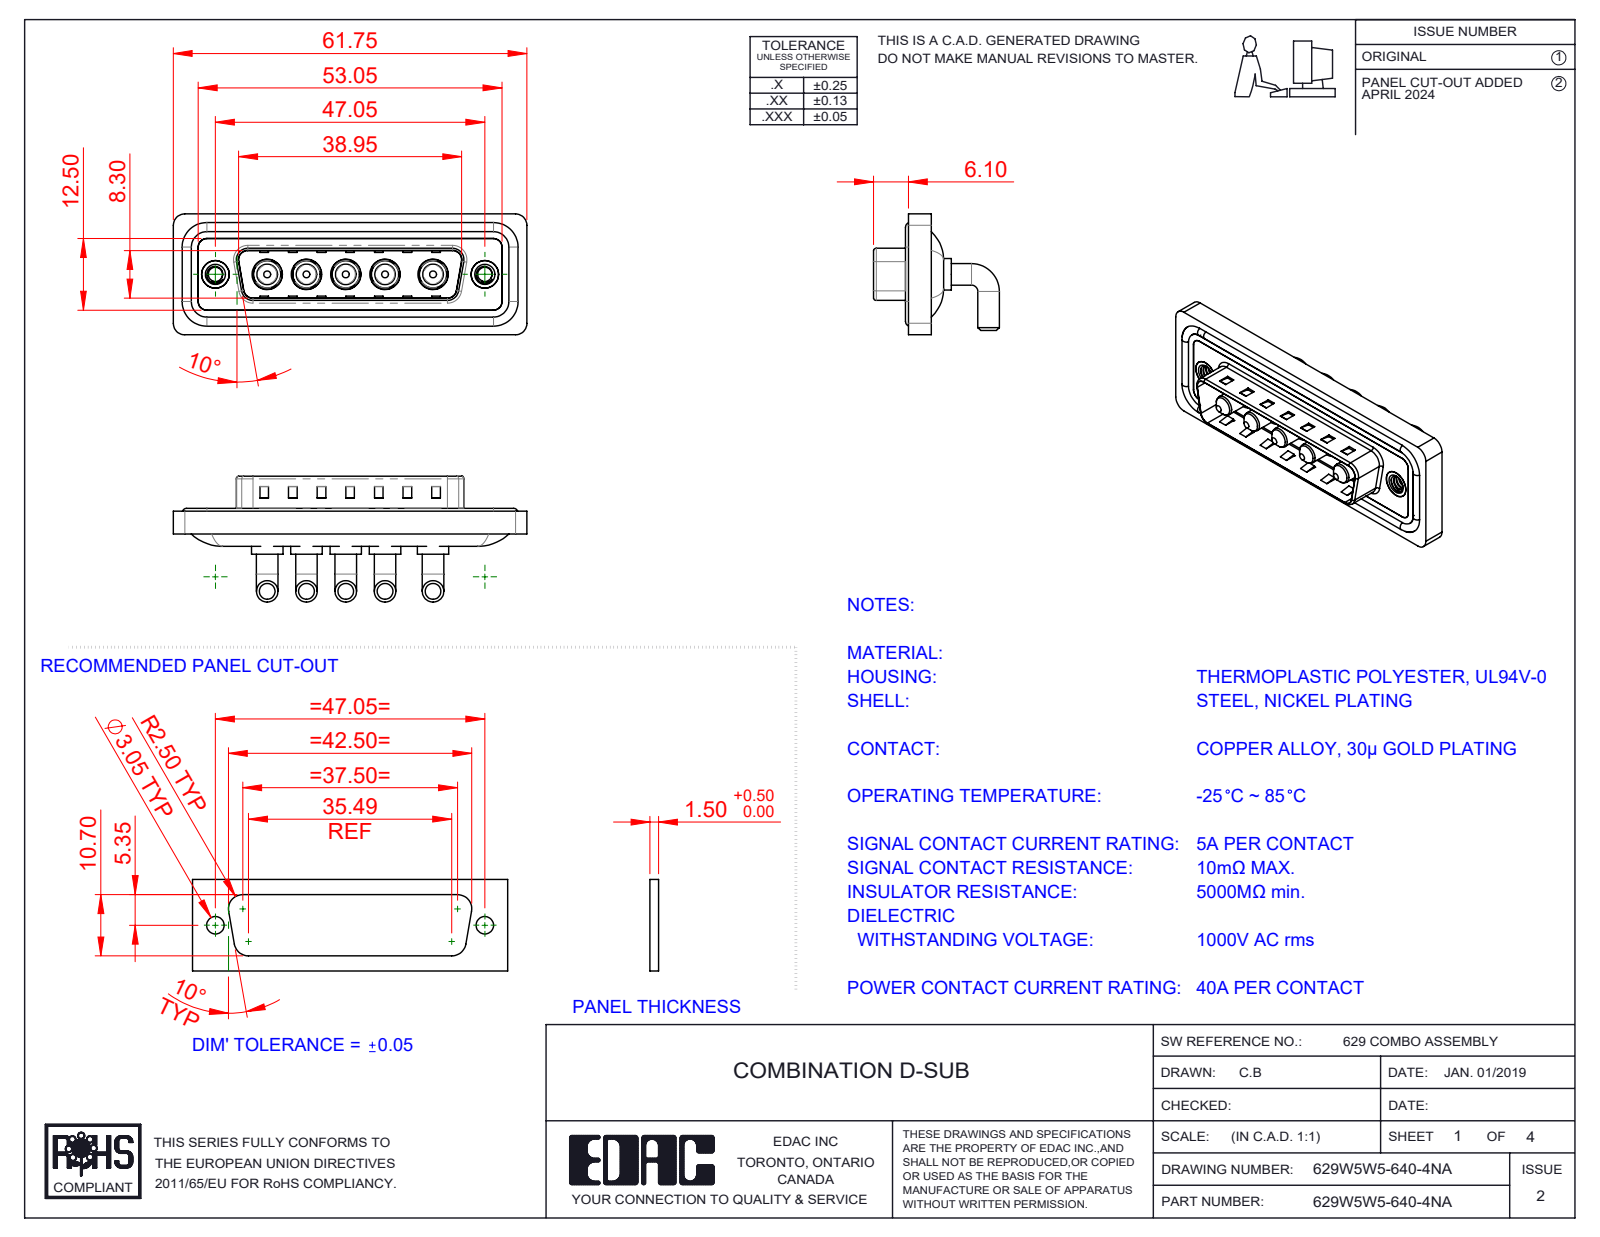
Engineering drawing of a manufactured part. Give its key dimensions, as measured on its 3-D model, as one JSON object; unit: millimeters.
{"part_name": "629Combo Shell Rear_25 Contacts; 629Combo Threaded Rivet_A; 629Combo Waterproof Housing_25 Contacts; 629Combo Shell Front_25 Contacts (+3 more)", "step_written_by": "SolidWorks 2023 (CONFIG_CONTROL_DESIGN)", "units": "millimeters", "bodies": {"solids": 17, "faces": 692, "planar": 259, "cylindrical": 291, "other": 142}, "overall_size": [61.75, 21.98, 21.1], "volume_mm3": 8170, "surface_area_mm2": 12495, "round_holes": [[4.85, 5], [5.3, 5], [2.5, 2], [4, 2], [4.8, 2], [5, 2]], "round_bosses_or_shafts": [[3.75, 10], [5.5, 5], [5.2, 5], [4.75, 5], [3.6, 5], [1.6, 4], [4.9, 2]], "partial_cylinders_radius": [[1.5, 18], [2, 18], [0.5, 8], [1.6, 8], [2.1, 5], [0.25, 4], [0.6, 4], [0.65, 4]], "face_to_face_distances": [0.4, 2.9, 0.8, 4.5, 4.1, 1.1, 2.1, 3.1, 6, 2.5], "hole_center_spacings": [6.86, 13.73, 6.85, 6.87, 8.37, 8.38, 9.04, 9.05]}
